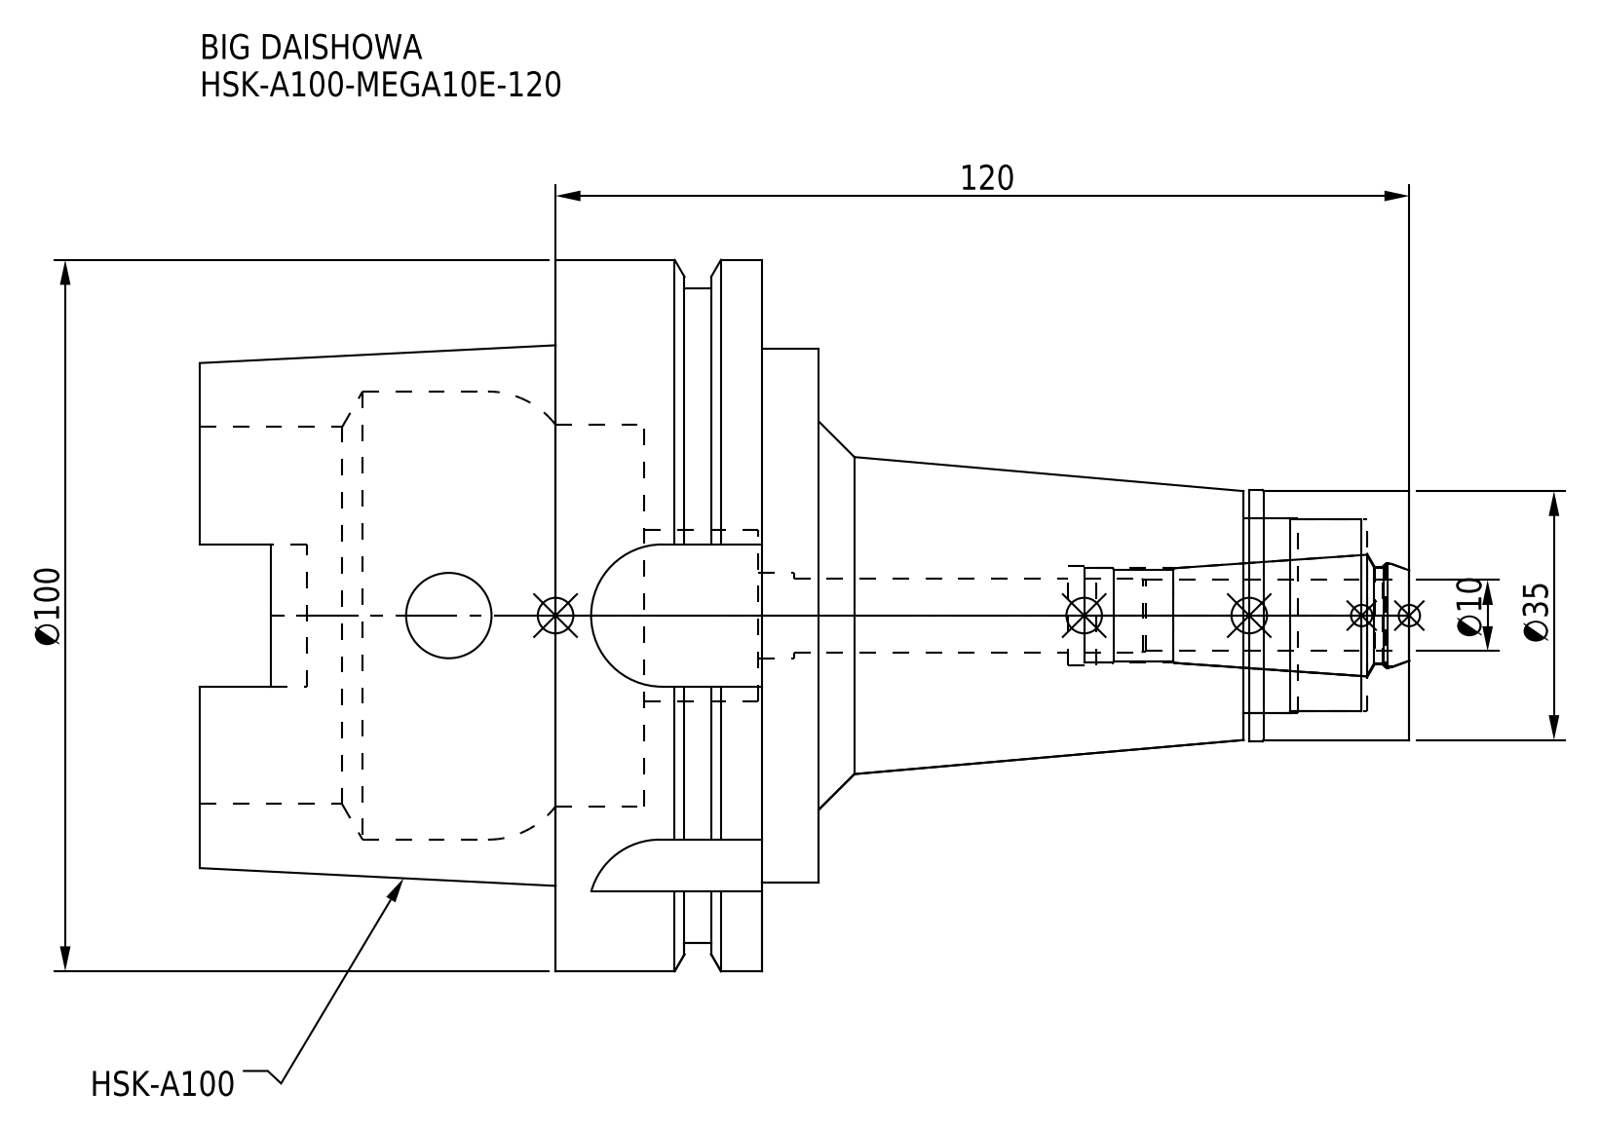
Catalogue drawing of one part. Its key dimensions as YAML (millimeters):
part_name: "MEN10_1.stp; HA100ME10120-100_ASM.stp; HSK-A100-MEGA10E-120_1.stp; DXF_TEMP_ASSY_ASM_4_ASM.stp (+3 more)"
step_written_by: "SolidWorks 2019 (CONFIG_CONTROL_DESIGN)"
units: millimeters
bodies: {solids: 2, faces: 126, planar: 42, cylindrical: 56, other: 28}
overall_size: [170, 100, 100]
volume: 377041
surface_area: 68801
round_holes:
  - {diameter: 12, count: 2}
  - {diameter: 10.4, count: 1}
  - {diameter: 13.3, count: 1}
  - {diameter: 13.8, count: 1}
  - {diameter: 13.9, count: 1}
  - {diameter: 14.7, count: 1}
  - {diameter: 24, count: 1}
  - {diameter: 27, count: 1}
  - {diameter: 27.5, count: 1}
  - {diameter: 53, count: 1}
  - {diameter: 53.8, count: 1}
  - {diameter: 63, count: 1}
round_bosses_or_shafts:
  - {diameter: 100, count: 1}
  - {diameter: 92, count: 1}
  - {diameter: 75, count: 1}
  - {diameter: 35.3, count: 1}
  - {diameter: 35, count: 1}
partial_cylinders:
  - {radius: 4.88, count: 4}
  - {radius: 10, count: 4}
face_to_face_distances: [29, 8, 37, 24.55, 16.55, 12.45, 87, 79, 62.45, 50]
